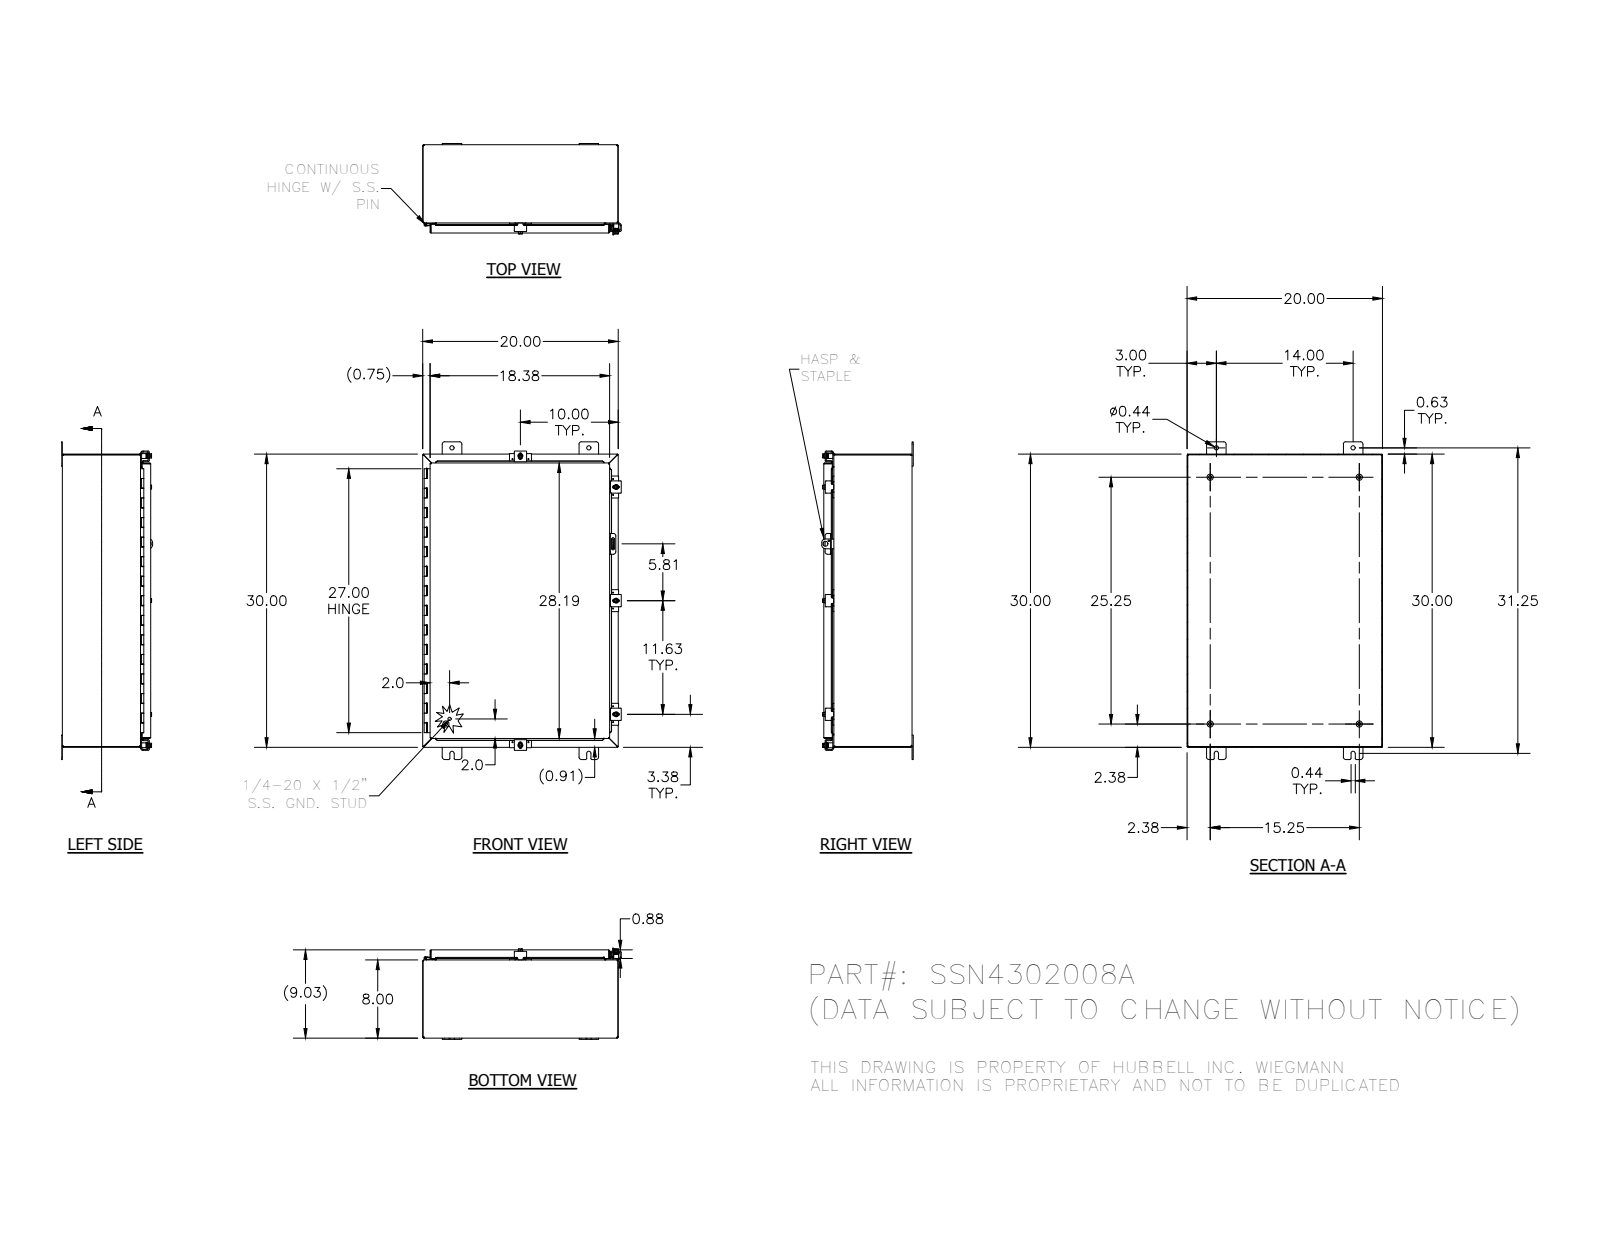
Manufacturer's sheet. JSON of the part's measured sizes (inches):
{"part_name": "30824-2; 30824-4; 32874-30L; 38846 (+8 more)", "step_written_by": "SolidWorks 2014 (AUTOMOTIVE_DESIGN)", "units": "inches", "bodies": {"solids": 42, "faces": 1722, "planar": 696, "cylindrical": 743, "other": 283}, "overall_size": [32.5, 20.216, 9.355], "volume_in3": 181.9, "surface_area_in2": 4780, "round_holes": [[0.11, 10], [0.211, 5], [0.281, 5], [0.3, 5], [0.438, 4], [0.125, 1], [0.156, 1], [0.5, 1]], "round_bosses_or_shafts": [[0.25, 7], [0.52, 5], [0.5, 5], [0.35, 5], [0.625, 4], [0.33, 4], [0.337, 1], [0.12, 1]], "partial_cylinders_radius": [[0.03, 61], [0.125, 35], [0.25, 31], [0.031, 23], [0.105, 23], [0.062, 16], [0.141, 10], [0.07, 8]], "face_to_face_distances": [0.074, 8.959, 8.885, 9.033, 19.926, 29.926, 7.926, 1.033, 20, 19.852], "hole_center_spacings": [0.876, 0.876, 9.438, 10.818, 10.998, 11.625, 11.625, 12.442]}
